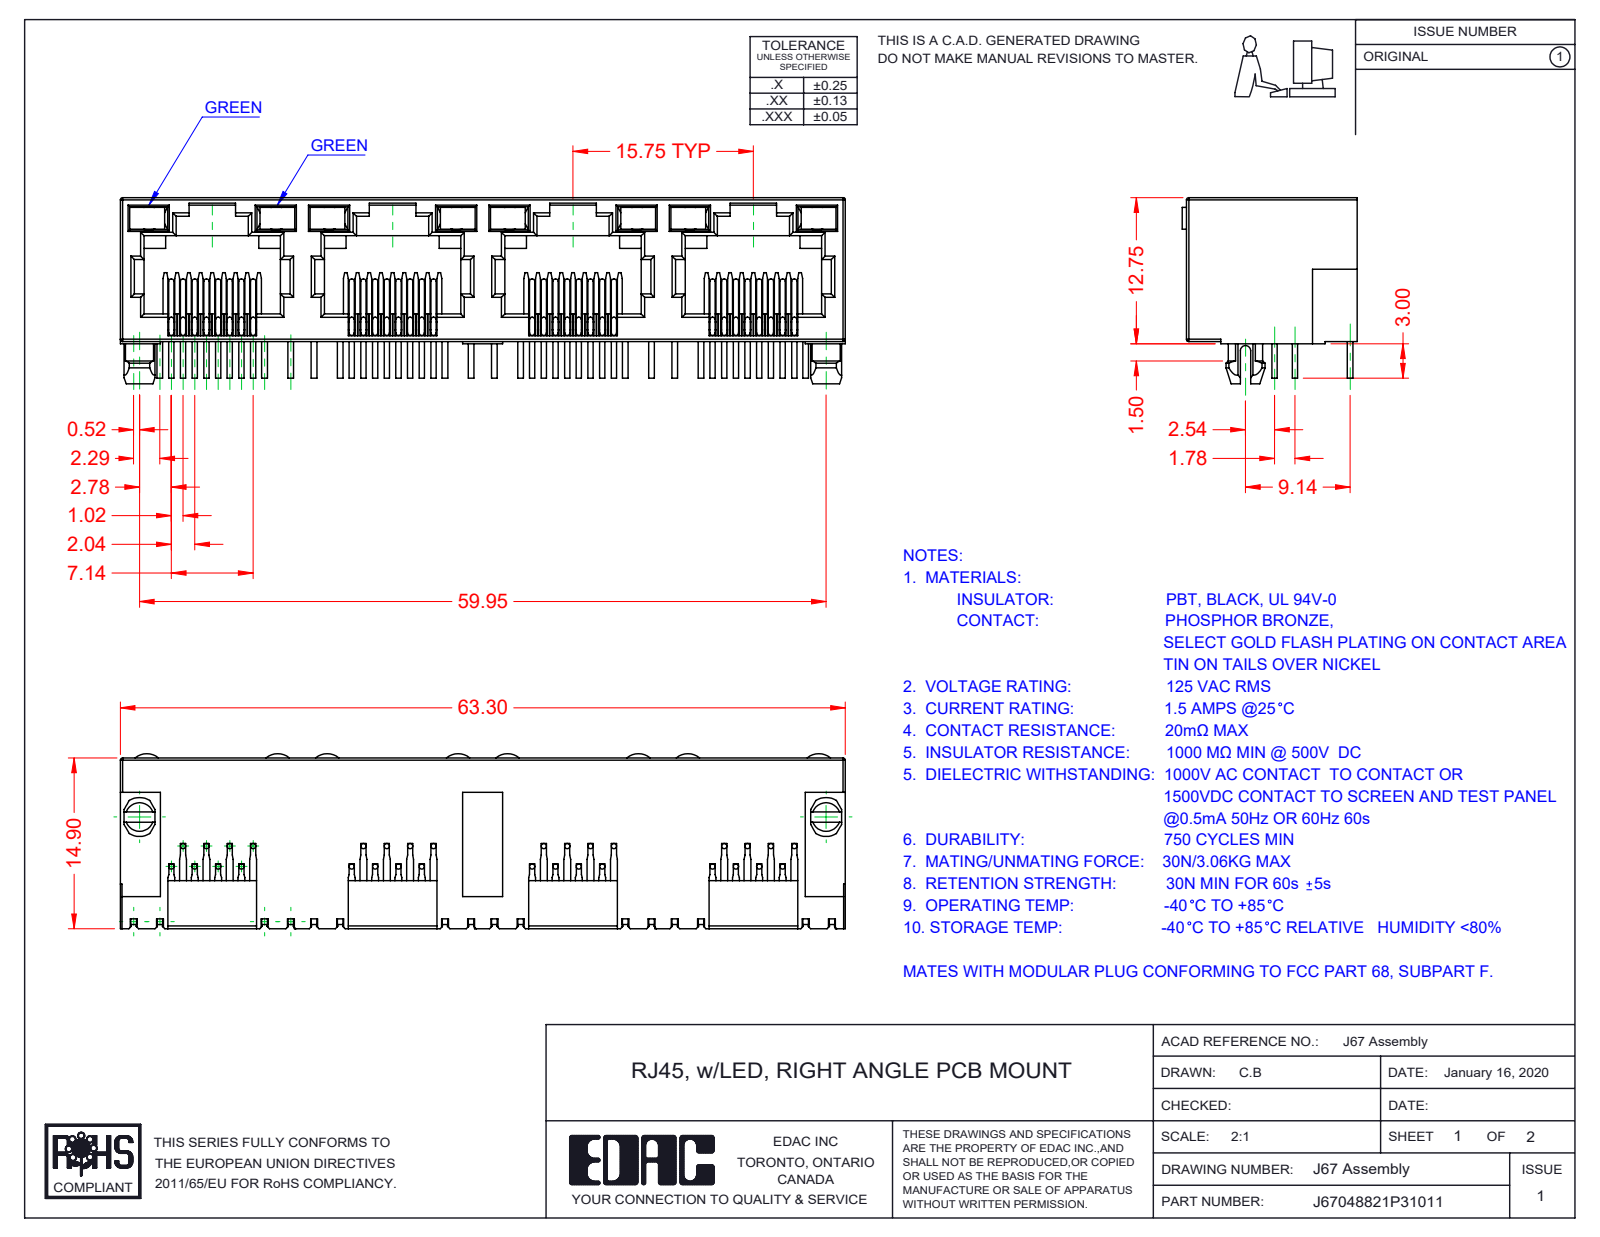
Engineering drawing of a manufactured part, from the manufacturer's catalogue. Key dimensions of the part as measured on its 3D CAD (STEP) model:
Part name (STEP PRODUCT): 67 Insulator; 67 LED LH_3-Green; J67048822P33011; 67 LED RH_3-Green (+1 more)
STEP written by: SolidWorks 2016 (CONFIG_CONTROL_DESIGN)
Units: millimetres
Bodies: 41 solids, 2465 faces (1781 planar, 476 cylindrical, 208 other)
Overall size (bounding box): 63.3 × 16.25 × 15.28
Volume: 5 159 mm³ · Surface area: 11 573 mm²
Round bosses / shafts (diameter × count): ⌀0.46 ×96
Partial cylindrical surfaces — rounded edges, fillets, slot ends (radius × count): R0.2 ×66, R0.3 ×29, R0.45 ×9, R1.55 ×8, R1.5 ×2, R1.7 ×2, R0.35 ×1, R1 ×1
Main face-to-face distances: 0.5, 12.55, 1.89, 0.89, 10, 15.75, 1, 1.39, 11, 11.89
